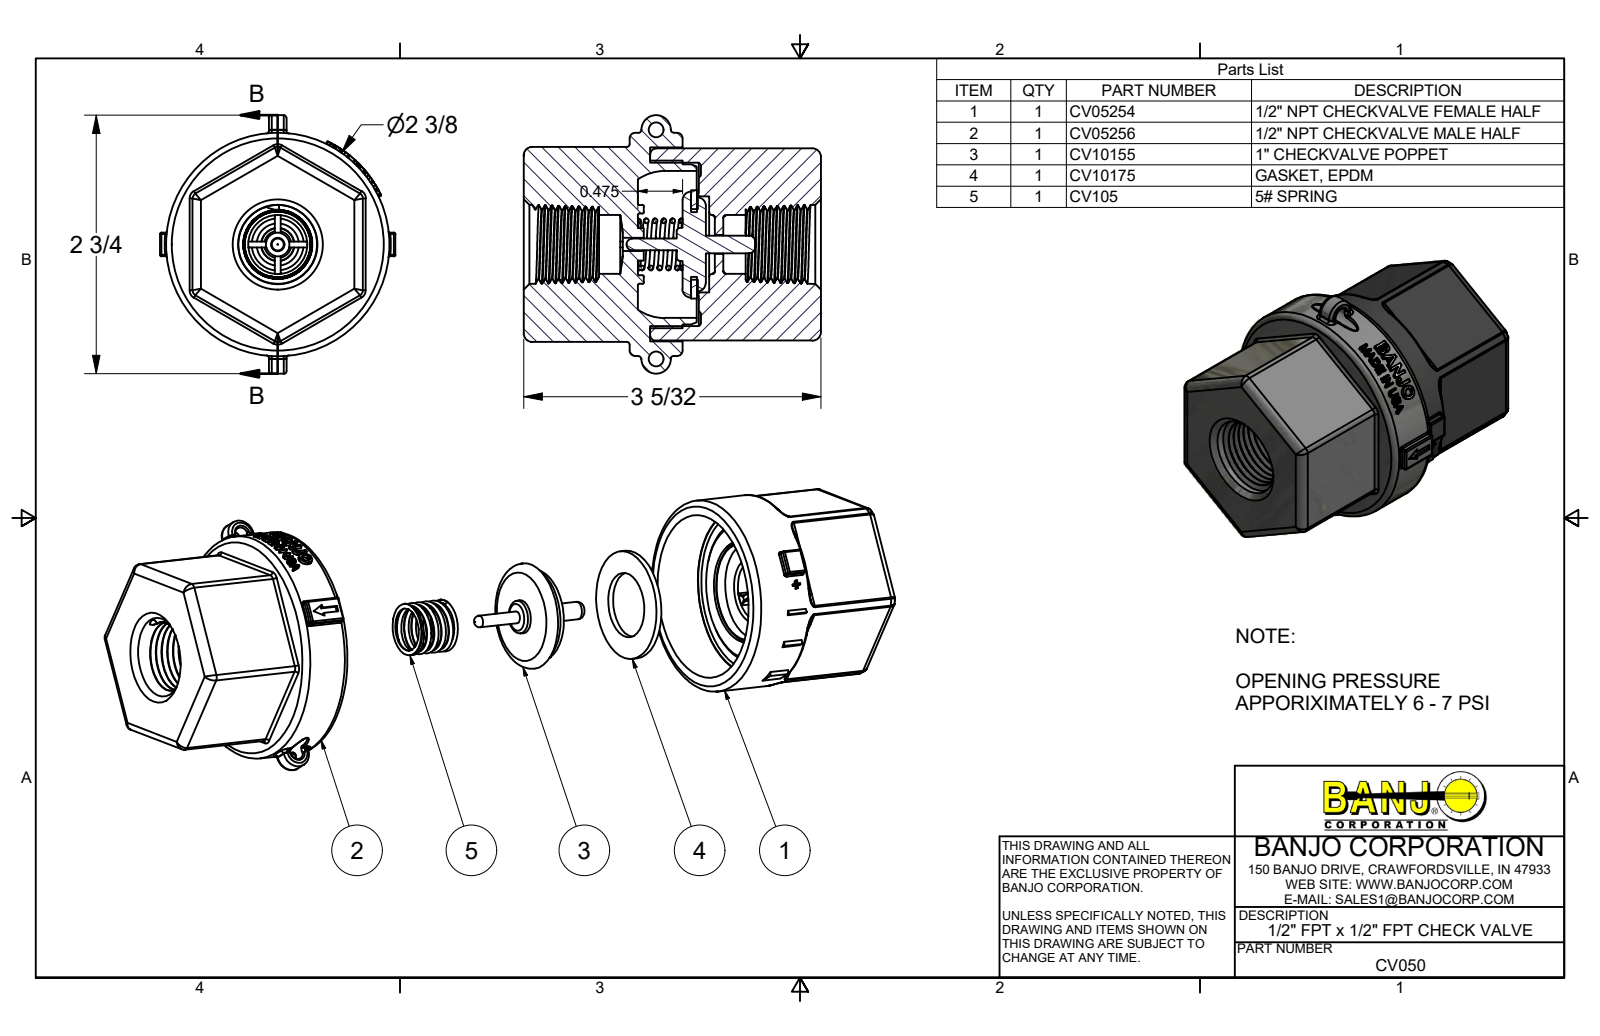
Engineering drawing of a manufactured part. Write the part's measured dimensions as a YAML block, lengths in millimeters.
part_name: "CV05256; CV05254X; CV05254; CV10155 (+3 more)"
step_written_by: "Autodesk Inventor 2016 (AUTOMOTIVE_DESIGN)"
units: millimeters
bodies: {solids: 5, faces: 847, planar: 236, cylindrical: 217, other: 394}
overall_size: [80.19, 69.77, 63.5]
volume: 127948
surface_area: 40828
round_holes:
  - {diameter: 3.97, count: 2}
  - {diameter: 3.56, count: 1}
  - {diameter: 5.08, count: 1}
  - {diameter: 15.88, count: 1}
  - {diameter: 17.46, count: 1}
  - {diameter: 25.91, count: 1}
  - {diameter: 39.65, count: 1}
  - {diameter: 44.07, count: 1}
  - {diameter: 52.32, count: 1}
round_bosses_or_shafts:
  - {diameter: 60.25, count: 1}
  - {diameter: 51.82, count: 1}
  - {diameter: 45.21, count: 1}
  - {diameter: 43.18, count: 1}
  - {diameter: 29.21, count: 1}
  - {diameter: 19.05, count: 1}
  - {diameter: 4.76, count: 1}
  - {diameter: 3.17, count: 1}
partial_cylinders:
  - {radius: 0.38, count: 48}
  - {radius: 0.76, count: 42}
  - {radius: 1.52, count: 12}
  - {radius: 2.29, count: 12}
  - {radius: 0.25, count: 8}
  - {radius: 3.97, count: 2}
  - {radius: 6.61, count: 2}
  - {radius: 3.17, count: 1}
face_to_face_distances: [45.98, 80.18, 34.13, 46.05, 44.95, 10.82, 35.23, 28.57, 51.61, 8.74]
hole_center_spacings: [61.84]
